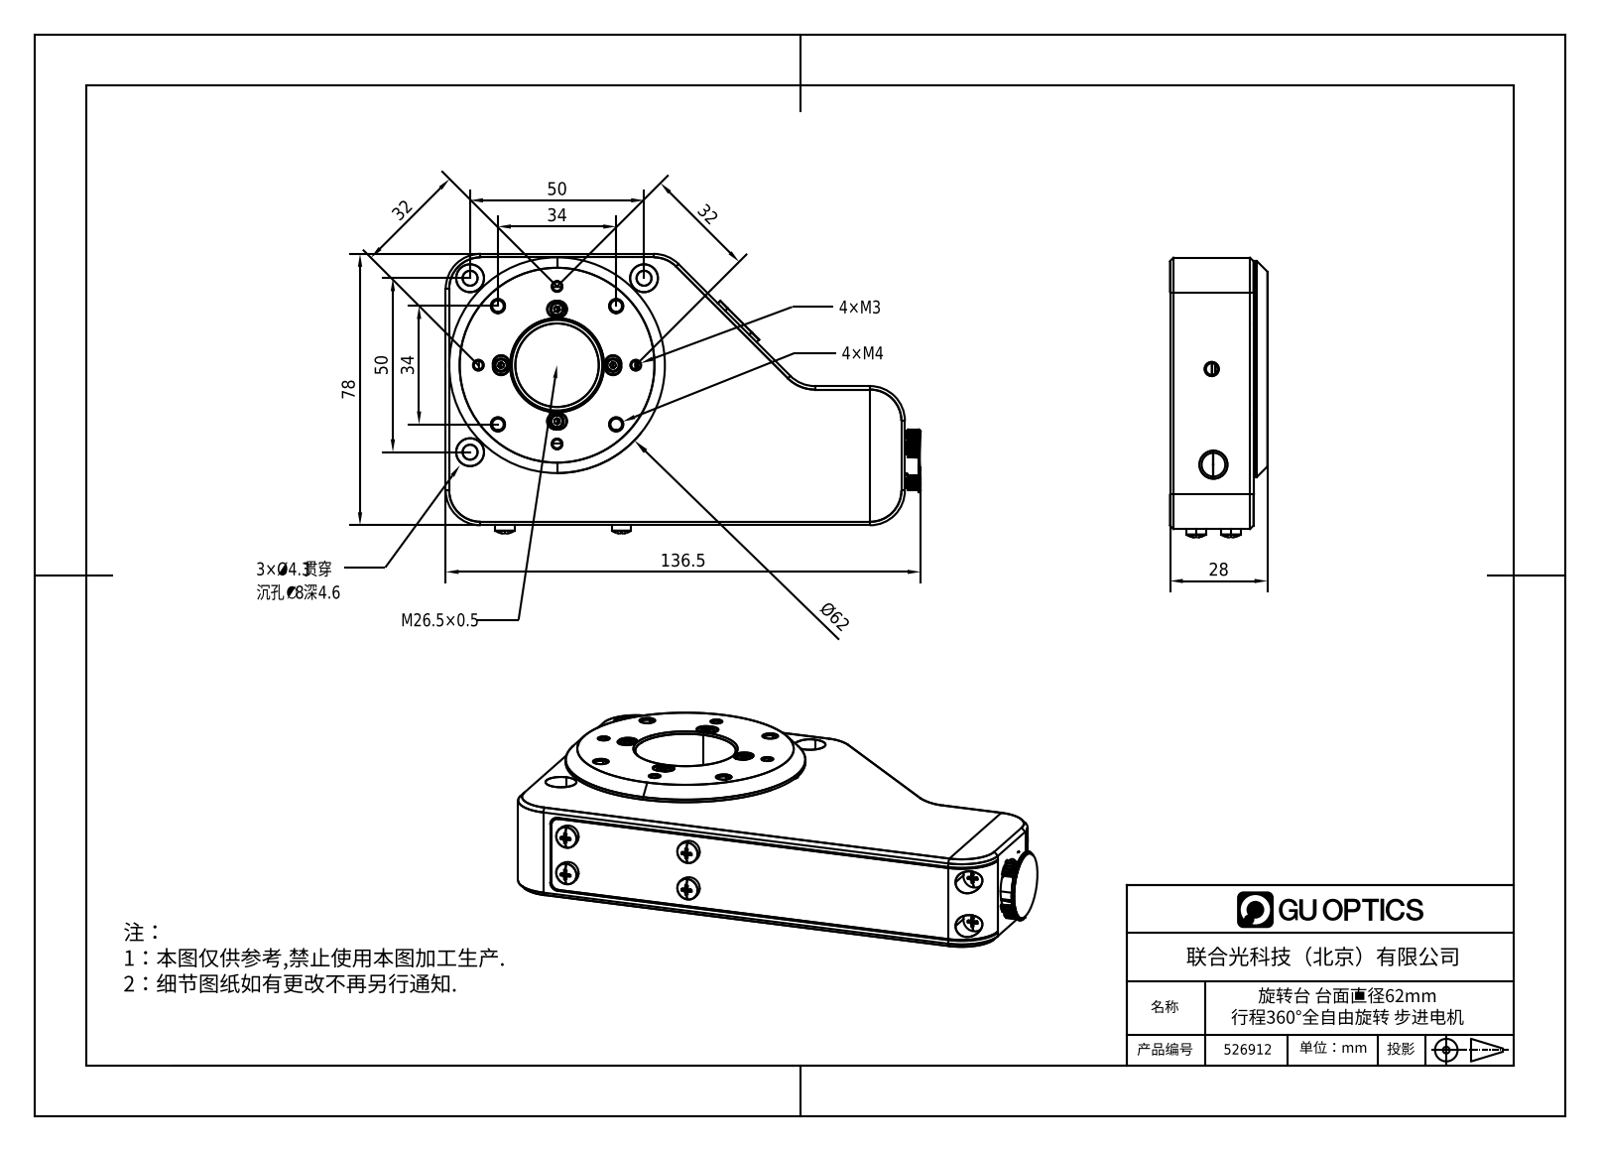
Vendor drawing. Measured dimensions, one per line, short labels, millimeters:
name: 526912
written by: SolidWorks 2020 (CONFIG_CONTROL_DESIGN)
unit: mm
bodies: 66 solids, 2645 faces (1434 planar, 744 cylindrical, 467 other)
size: 132 × 79.5 × 40.8
volume: 227 866 mm³; area: 116 100 mm²
holes: 26× ⌀2.5, 20× ⌀3.4, 15× ⌀6.5, 9× ⌀1.1, 8× ⌀1.6, 8× ⌀3, 8× ⌀3.3, 8× ⌀4.5, 8× ⌀8, 7× ⌀2.4, 4× ⌀5, 4× ⌀6
bosses: 24× ⌀5.5, 22× ⌀0.5, 20× ⌀3, 9× ⌀1.5, 9× ⌀1, 8× ⌀7, 8× ⌀4, 7× ⌀2
rounds: 46× R0.5, 28× R0.3, 25× R1, 14× R2, 8× R0.4, 8× R3, 5× R8, 4× R1.3
face distances: 5, 3, 2, 33, 10, 35, 30, 2.5, 20, 35.5
hole spacings: 21, 3.16, 2.77, 13.58, 32.34, 5.54, 13.43, 18.79
